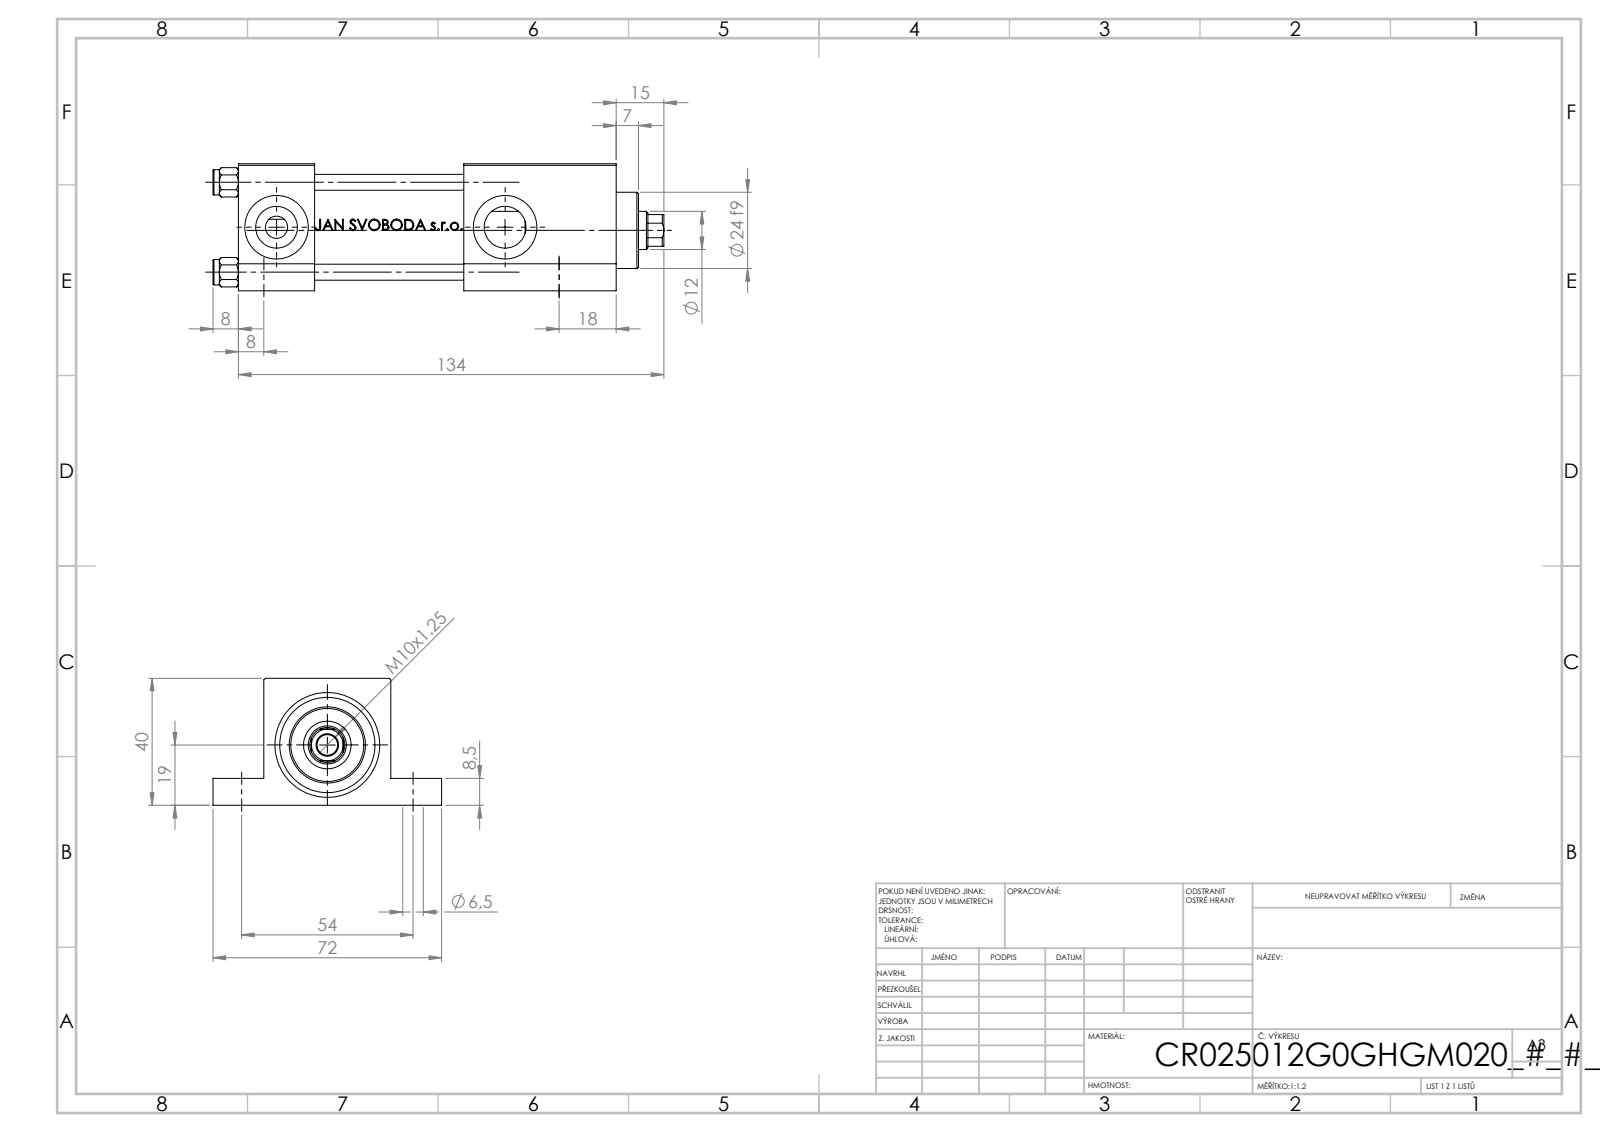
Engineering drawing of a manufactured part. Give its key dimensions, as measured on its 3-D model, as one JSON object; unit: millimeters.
{"part_name": "V215_VC_A; NUT_M5_G; V215CR_VCP_G; V215CR_G_TYCINKA (+1 more)", "step_written_by": "SolidWorks 2019 (CONFIG_CONTROL_DESIGN)", "units": "millimeters", "bodies": {"solids": 11, "faces": 1086, "planar": 430, "cylindrical": 124, "other": 532}, "overall_size": [142, 72, 40], "volume_mm3": 161747, "surface_area_mm2": 59769, "round_holes": [[6.5, 5], [5, 4], [20, 3], [7, 2], [13.16, 2], [12, 1], [15, 1], [25, 1], [30, 1]], "round_bosses_or_shafts": [[8, 4], [31, 1], [24, 1]], "partial_cylinders_radius": [[5.5, 1]], "face_to_face_distances": [40, 8.5, 31.5, 24, 119, 95, 16, 56, 48, 71], "hole_center_spacings": [28.3, 19.32, 20.73, 40.02, 54, 93, 107.54, 72]}
